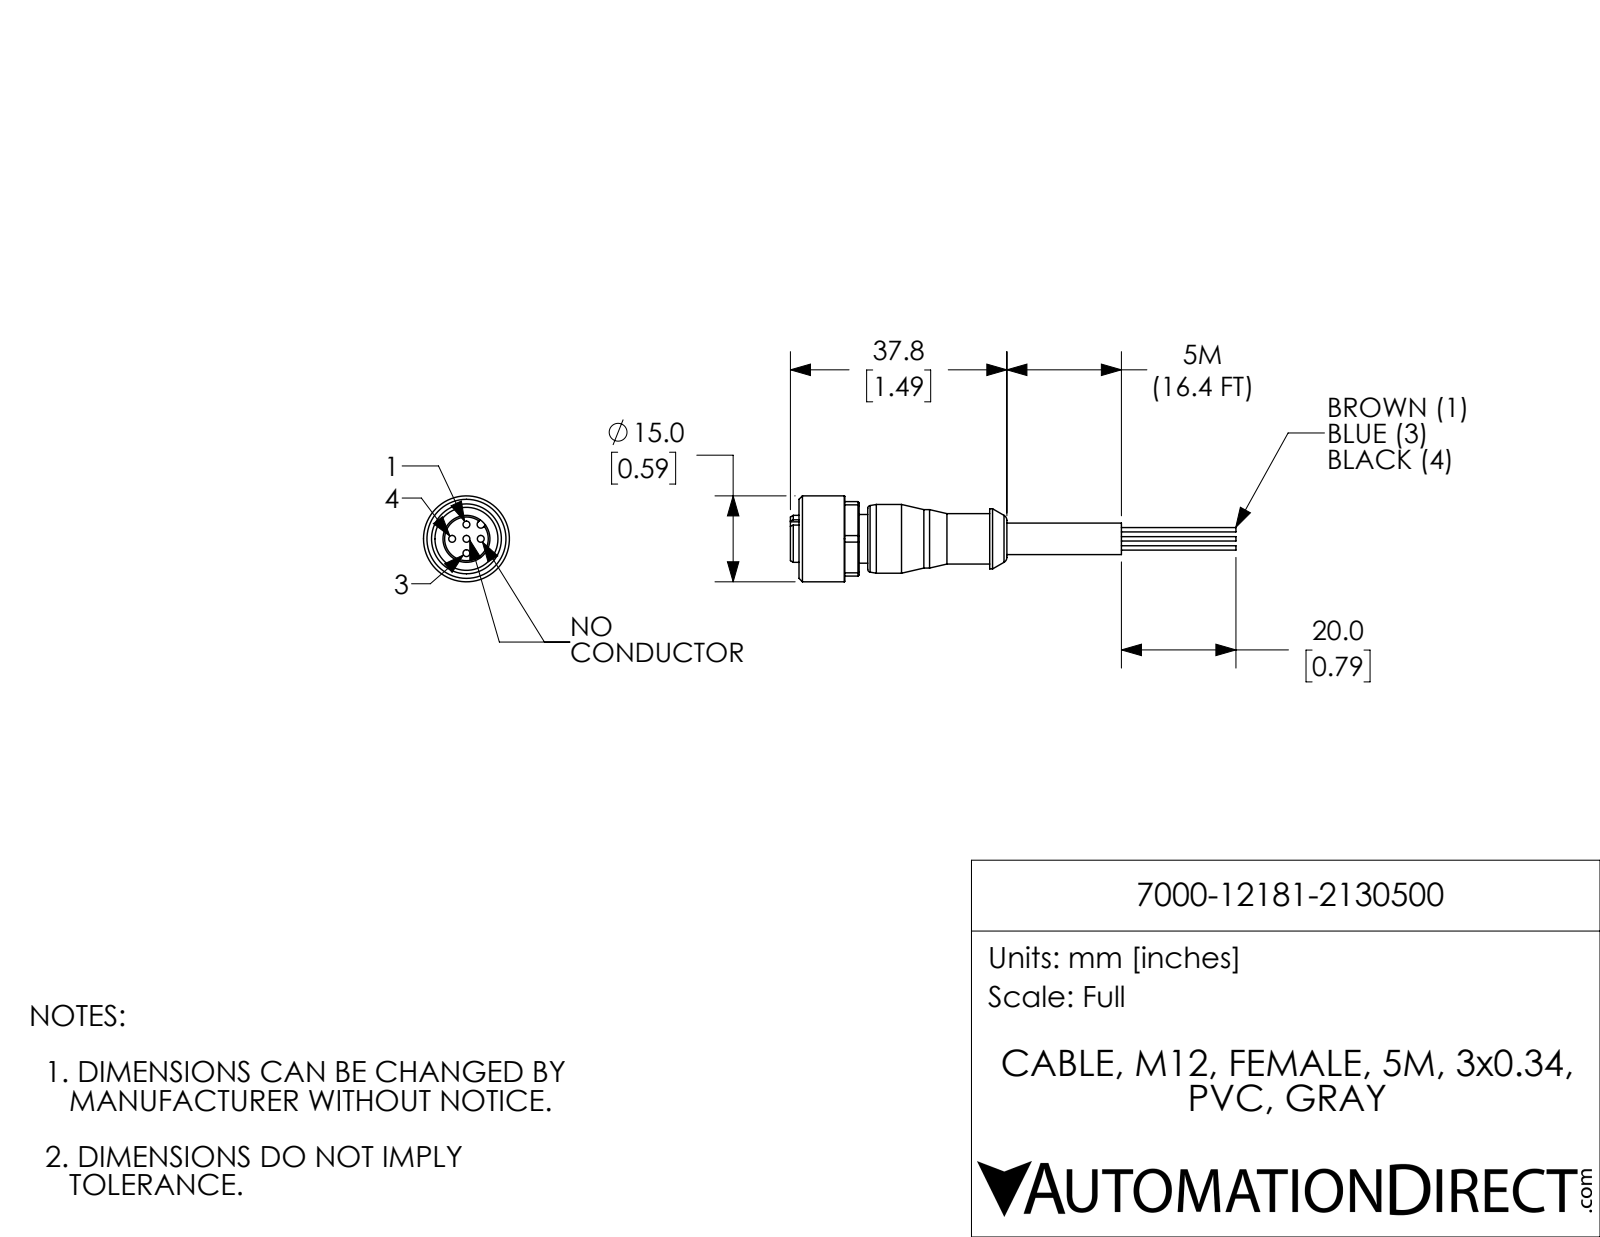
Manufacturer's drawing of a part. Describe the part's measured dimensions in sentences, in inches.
The part is named "7000-12181-2130500". Its 3-D file was written by "SolidWorks 2017 (AUTOMOTIVE_DESIGN)". It is 1 solid with 100 faces: 32 planar, 41 cylindrical and 27 other. Overall it measures 3.063 by 0.591 by 0.591 inches. Its volume is 0.247 cubic inches and its surface area 4.356 square inches. Round holes: 5 of diameter 0.047, 1 of diameter 0.433. Round bosses or shafts: 3 of diameter 0.03, 1 of diameter 0.591, 1 of diameter 0.472, 1 of diameter 0.413, 1 of diameter 0.402, 1 of diameter 0.346, 1 of diameter 0.335, 1 of diameter 0.323. Partial cylindrical surfaces (rounded edges, fillets, slot ends): 1 of radius 0.026, 1 of radius 0.283. The main face-to-face distances are 0.472, 0.059, 0.118, 0.512, 0.354, 1.016, 0.295, 0.413, 0.098, 0.531. The hole center spacings are 0.098, 0.139, 0.197.
